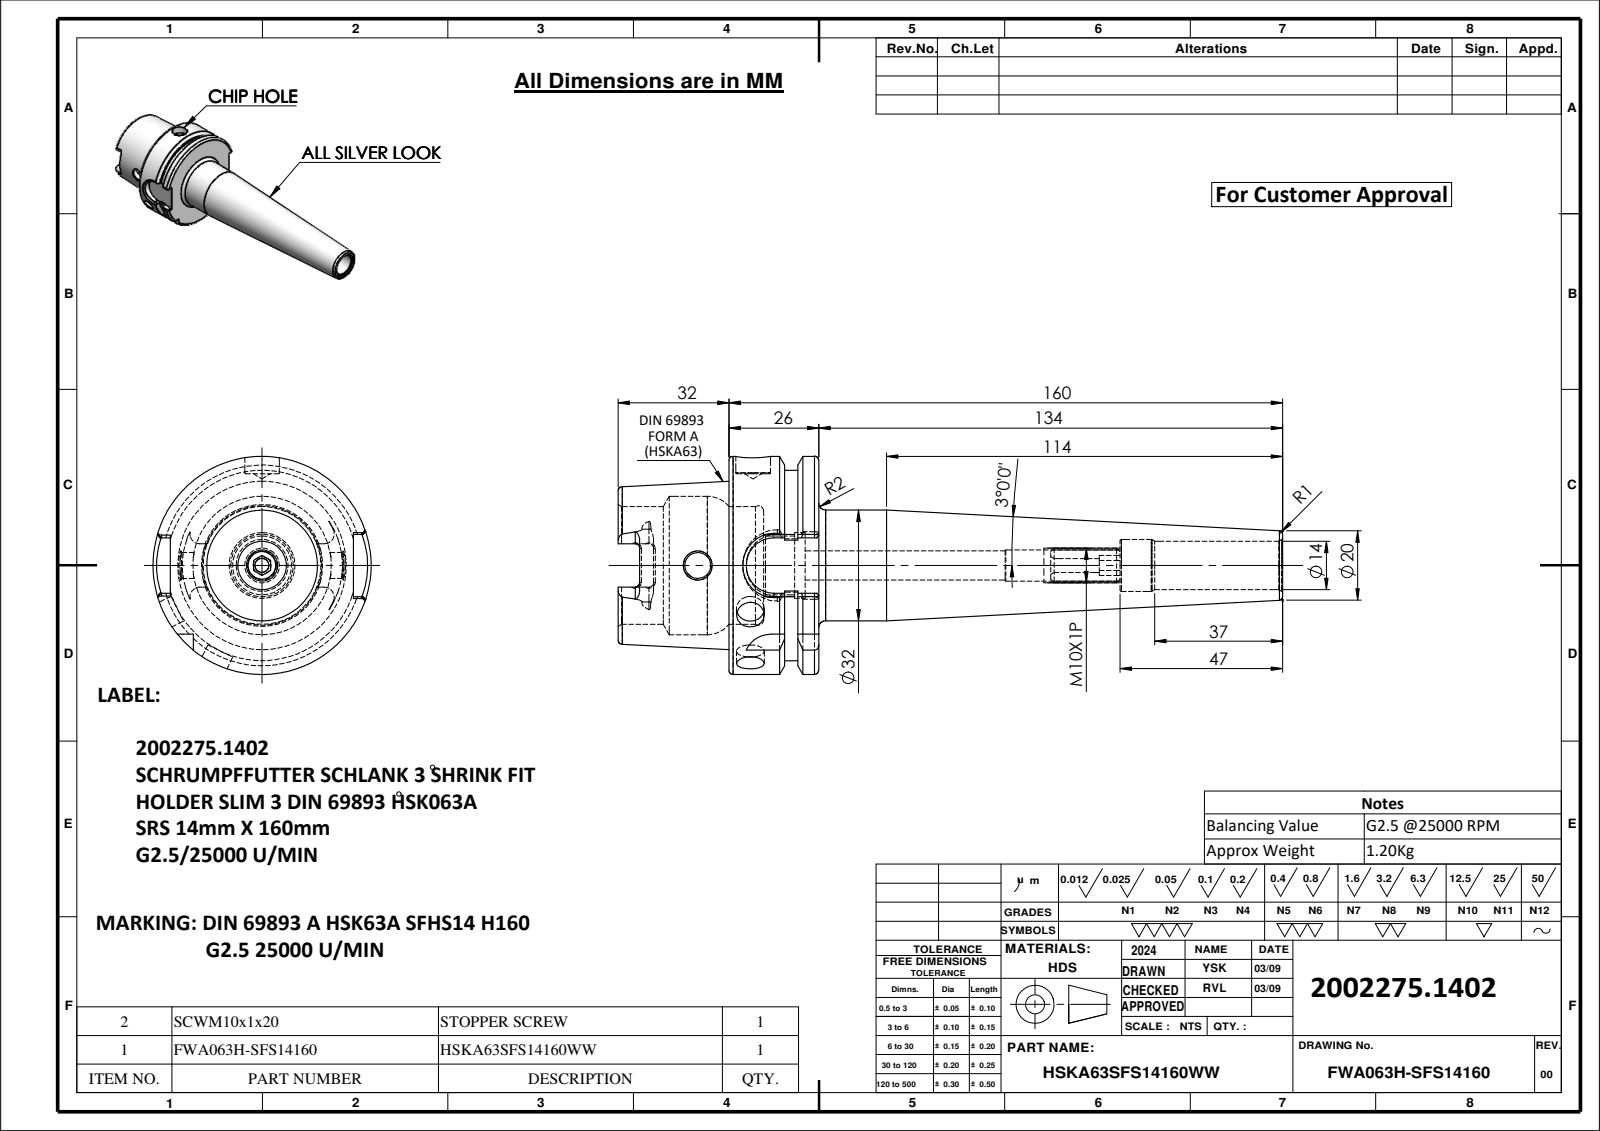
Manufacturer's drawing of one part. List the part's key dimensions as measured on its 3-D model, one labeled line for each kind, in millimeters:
Part name (STEP PRODUCT): FWA063H-SFS14160; SCWM10X1; HSKA63SFS14160WW
STEP written by: SolidWorks 2024 (CONFIG_CONTROL_DESIGN)
Units: millimetres
Bodies: 2 solids, 196 faces (59 planar, 57 cylindrical, 80 other)
Overall size (bounding box): 192 × 63 × 63
Volume: 147 154 mm³ · Surface area: 38 519 mm²
Round holes (diameter × count): ⌀8 ×2, ⌀4 ×1, ⌀7.5 ×1, ⌀8.4 ×1, ⌀9 ×1, ⌀10 ×1, ⌀14 ×1, ⌀15 ×1, ⌀17 ×1, ⌀19 ×1, ⌀34 ×1, ⌀40 ×1
Round bosses / shafts (diameter × count): ⌀63 ×1, ⌀55 ×1, ⌀32 ×1, ⌀10 ×1
Partial cylindrical surfaces — rounded edges, fillets, slot ends (radius × count): R1.3 ×6, R2.88 ×4, R8 ×2, R9 ×1
Main face-to-face distances: 25.95, 10, 15.95, 32, 42, 57.95, 52.9, 54, 22, 12
